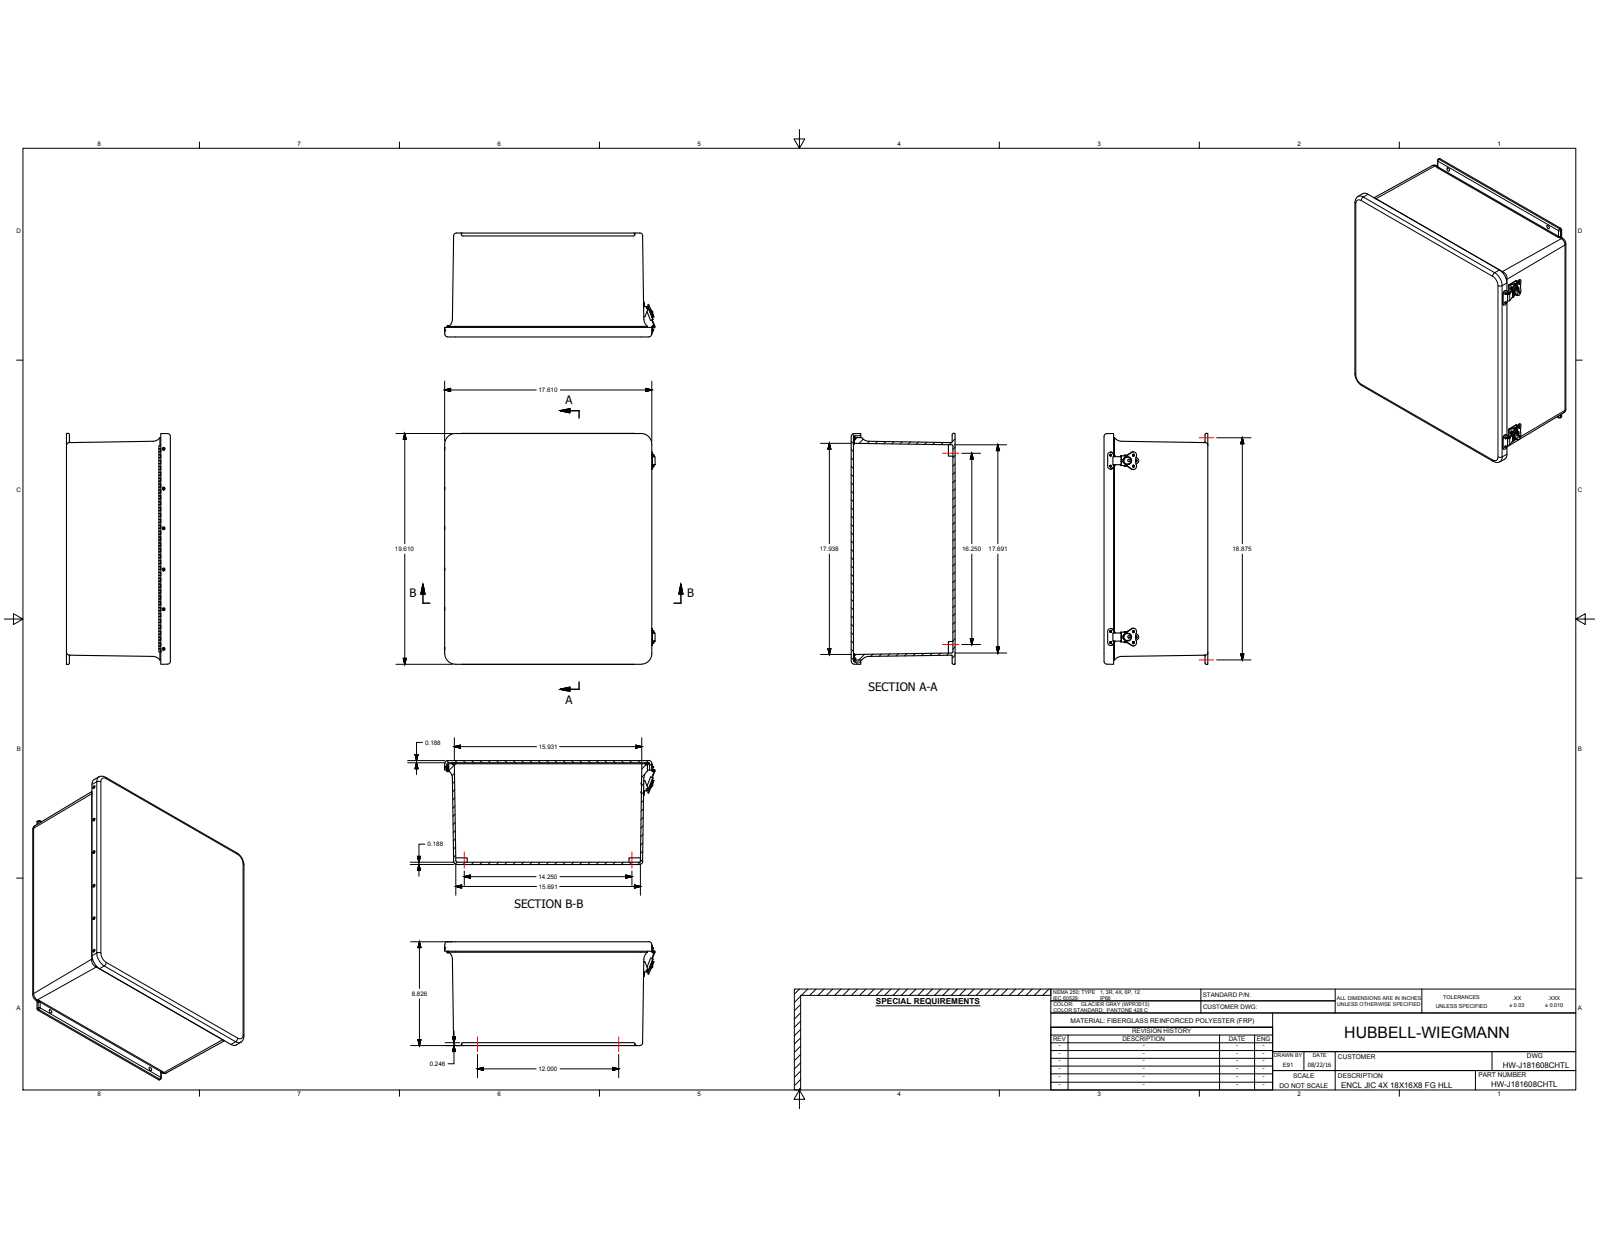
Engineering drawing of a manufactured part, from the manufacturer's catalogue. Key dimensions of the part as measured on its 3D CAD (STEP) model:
Part name (STEP PRODUCT): HW-J1816CHTL; WP1816HLBOX; WP1816HLU; WP1816HLCVR (+8 more)
STEP written by: Autodesk Inventor 2017 (CONFIG_CONTROL_DESIGN)
Units: millimetres
Bodies: 46 solids, 1147 faces (558 planar, 469 cylindrical, 120 other)
Overall size (bounding box): 498.6 × 454.51 × 224.17
Volume: 4 271 000 mm³ · Surface area: 1 763 000 mm²
Round holes (diameter × count): ⌀3.56 ×22, ⌀2.64 ×20, ⌀3.33 ×12, ⌀3.86 ×8, ⌀3.3 ×4, ⌀3.38 ×4, ⌀4.75 ×4, ⌀5.54 ×4, ⌀7.92 ×4, ⌀3.43 ×2, ⌀4.8 ×2, ⌀4.85 ×2
Round bosses / shafts (diameter × count): ⌀3.17 ×20, ⌀16.76 ×2, ⌀14.78 ×2, ⌀13.34 ×2, ⌀7.26 ×2, ⌀5.41 ×2, ⌀4.57 ×2, ⌀3.18 ×2
Partial cylindrical surfaces — rounded edges, fillets, slot ends (radius × count): R3.17 ×17, R0.38 ×16, R1.52 ×13, R6.35 ×10, R0.29 ×8, R0.51 ×8, R1.4 ×8, R1.78 ×8
Main face-to-face distances: 4.76, 224.17, 219.41, 4.77, 219.4, 214.64, 12.44, 7.68, 6.68, 1.92
Hole centre spacings: 380.6, 85.72, 85.73, 171.45, 380.62, 3.99, 260.35, 6.35
